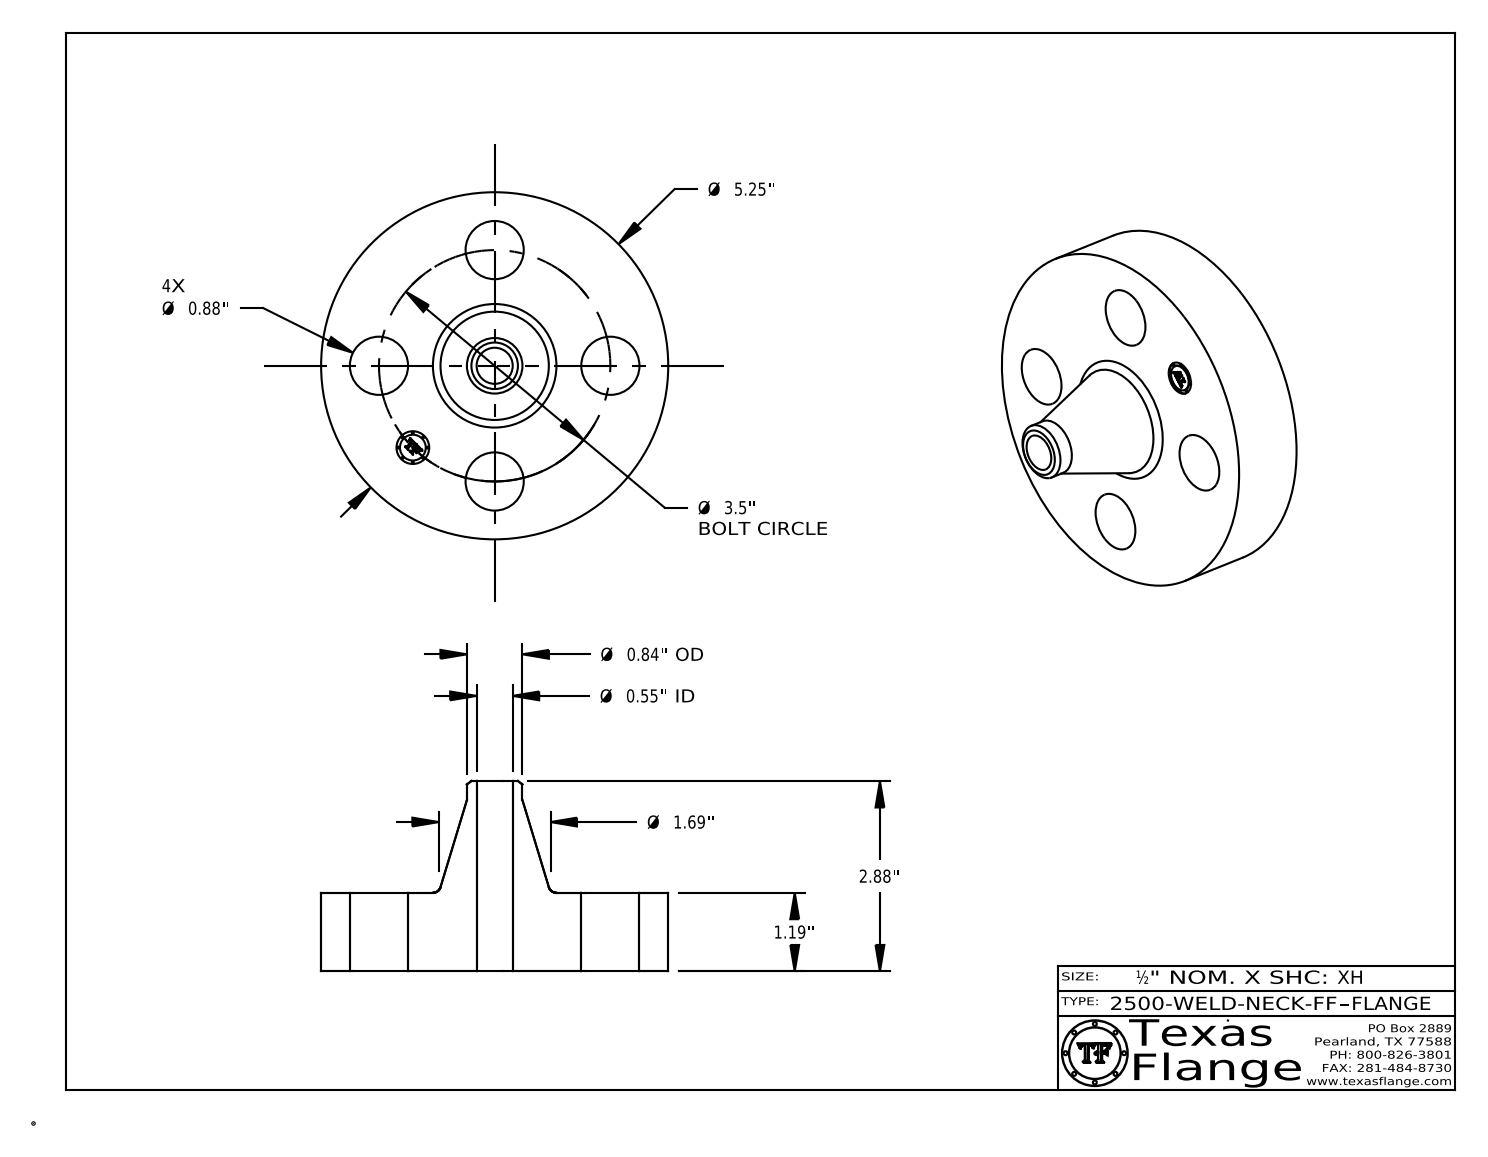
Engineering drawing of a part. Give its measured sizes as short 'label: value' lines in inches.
name: 2500-WELD-NECK-FF
written by: CATIA V5 STEP AP214 (AUTOMOTIVE_DESIGN)
unit: in
bodies: 1 solid, 408 faces (368 planar, 34 cylindrical, 6 other)
size: 5.25 × 5.25 × 2.88
volume: 24.18 in³; area: 80.45 in²
holes: 4× ⌀0.88, 1× ⌀0.495, 1× ⌀0.546
bosses: 8× ⌀0.03, 1× ⌀5.25, 1× ⌀0.84, 1× ⌀0.39
face distances: 1.19, 2.88, 1.69, 1.175, 0.015, 1.705, 0.148, 0.145, 0.027, 0.096
hole spacings: 1.75, 2.475, 1.339, 3.233, 3.5
